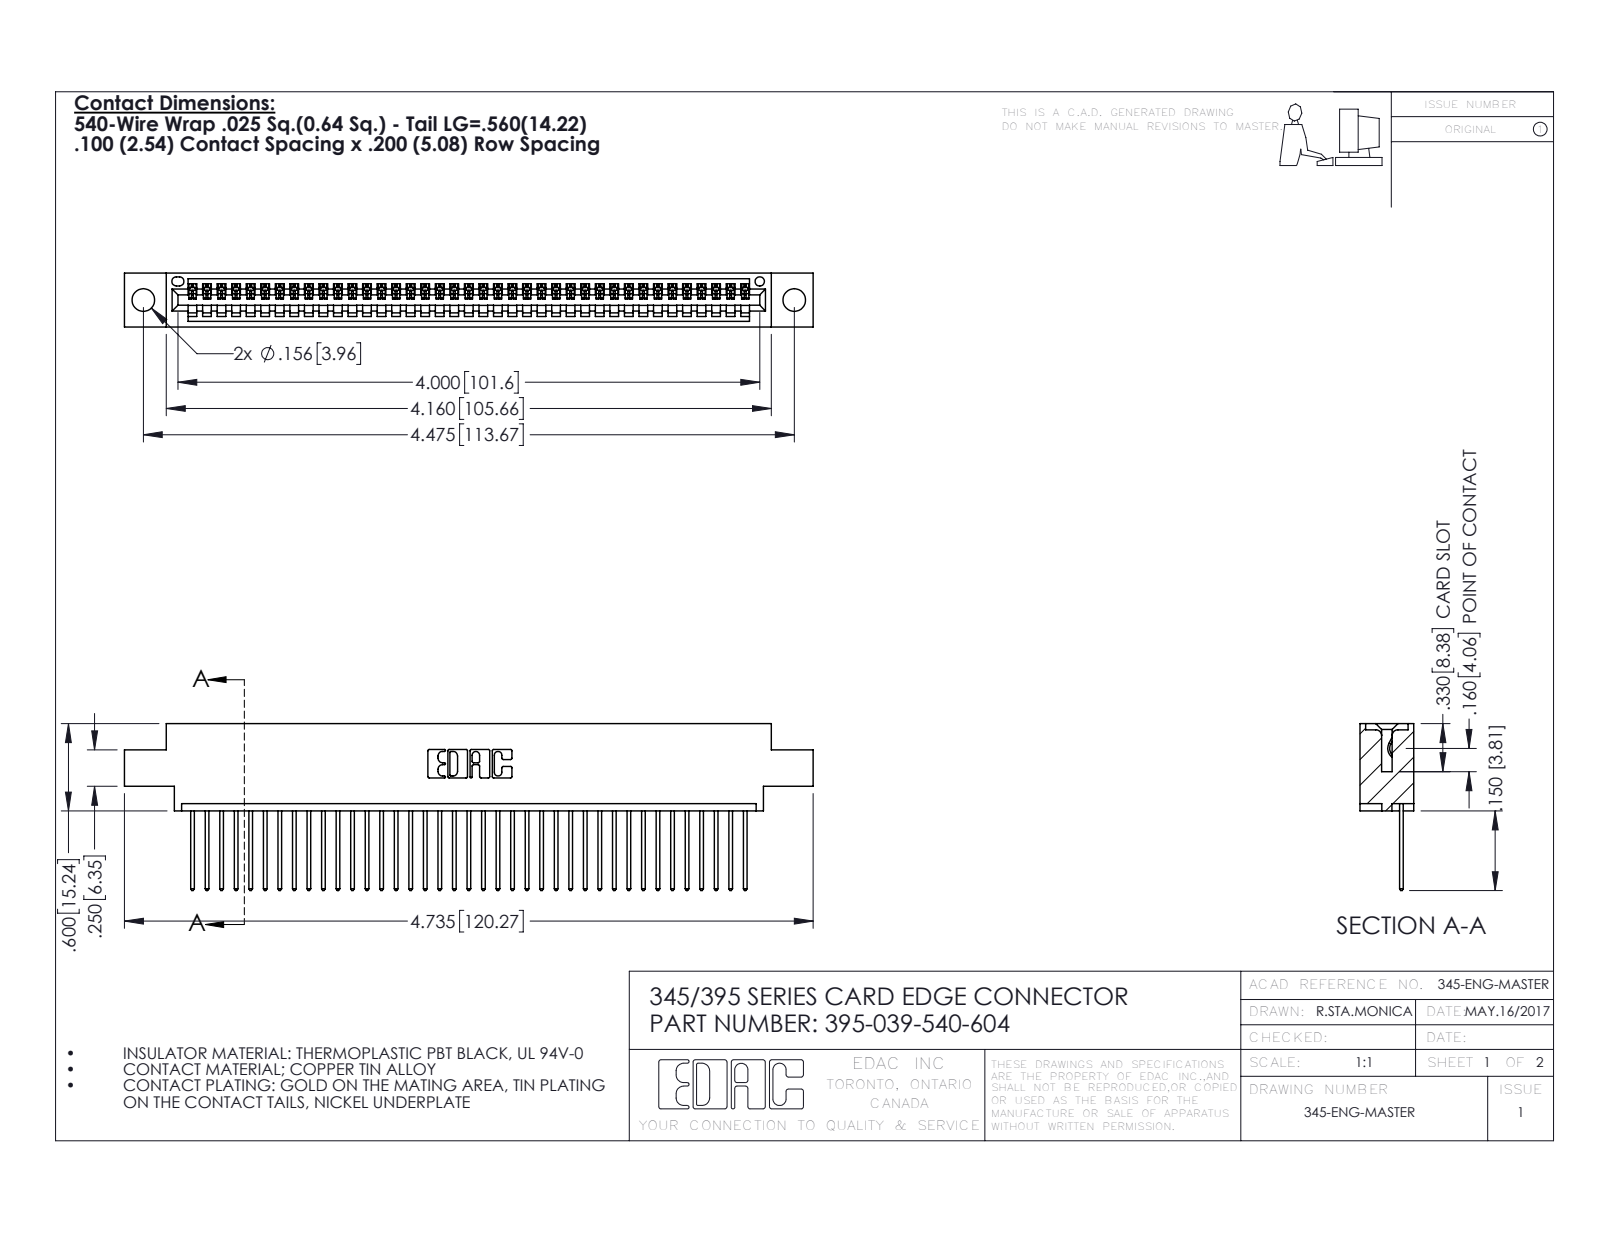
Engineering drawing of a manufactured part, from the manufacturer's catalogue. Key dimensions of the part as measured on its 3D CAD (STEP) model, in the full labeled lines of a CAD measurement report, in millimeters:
Part name (STEP PRODUCT): 345 Part_0.170 Offset - 0.156 Dia-TH; 345-292-001_345-293-140; 395-039-540-604
STEP written by: SolidWorks 2016 (CONFIG_CONTROL_DESIGN)
Units: millimetres
Bodies: 40 solids, 2392 faces (1644 planar, 748 cylindrical, 0 other)
Overall size (bounding box): 120.3 × 29.1 × 9.4
Volume: 11 300 mm³ · Surface area: 15 230 mm²
Round holes (diameter × count): ⌀4 ×2, ⌀1.6 ×1
Partial cylindrical surfaces — rounded edges, fillets, slot ends (radius × count): R0.2 ×78, R0.3 ×78, R0.3 ×22, R0.2 ×6, R0.8 ×6, R0.7 ×3, R0.8 ×2, R1 ×2
Main face-to-face distances: 7.6, 1.8, 9.4, 2.5, 6.9, 0.6, 5.1, 5.7, 4.4, 3.8
Hole centre spacings: 6.9, 107.7, 113.7
